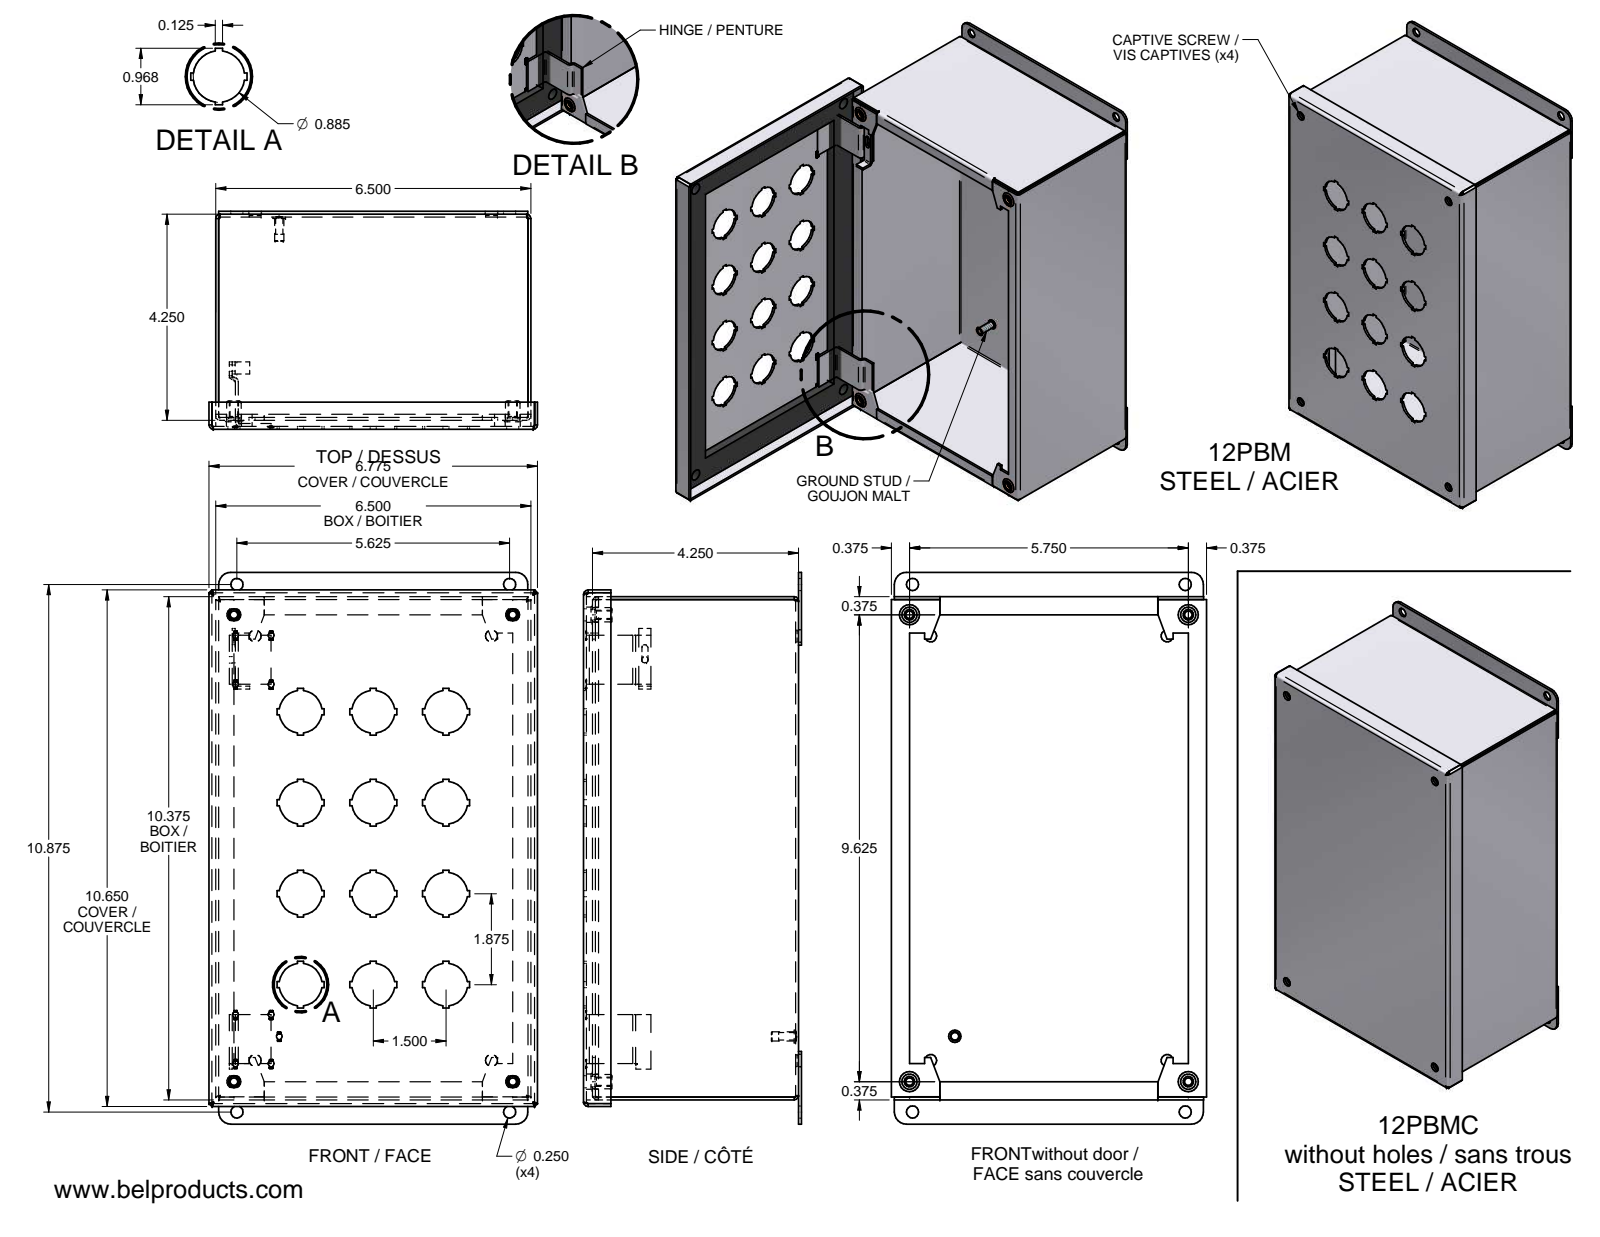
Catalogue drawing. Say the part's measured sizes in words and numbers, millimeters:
The part is named "12PBM_BOITIER; 12PBM-B; INSERT 10-32 AVK ALS4-1032-130; 12PBM-P (+7 more)". Its 3-D file was written by "Unknown (AUTOMOTIVE_DESIGN)". It is 13 solids with 1478 faces: 1043 planar, 154 cylindrical and 281 other. Overall it measures 288.93 by 172.09 by 114.17 millimeters. Its volume is 409 111 cubic millimeters and its surface area 463 066 square millimeters. Round holes: 12 of diameter 22.48, 9 of diameter 3.17, 8 of diameter 6.35, 4 of diameter 4.04, 4 of diameter 5.49, 4 of diameter 6.22, 4 of diameter 6.73, 4 of diameter 7.37, 4 of diameter 7.92, 1 of diameter 3.45. Round bosses or shafts: 9 of diameter 3.02, 4 of diameter 7.52, 4 of diameter 6.35, 1 of diameter 6.5, 1 of diameter 4.83, 1 of diameter 0.51. Partial cylindrical surfaces (rounded edges, fillets, slot ends): 16 of radius 0.81, 16 of radius 2.34, 4 of radius 6.35, 2 of radius 1.59. The main face-to-face distances are 1.52, 111.13, 163.58, 112.65, 1.53, 109.6, 111.12, 262, 165.1, 162.06. The hole center spacings are 38.09, 60.99, 102.58, 15.95, 47.63, 89.84, 95.25, 122.56.
